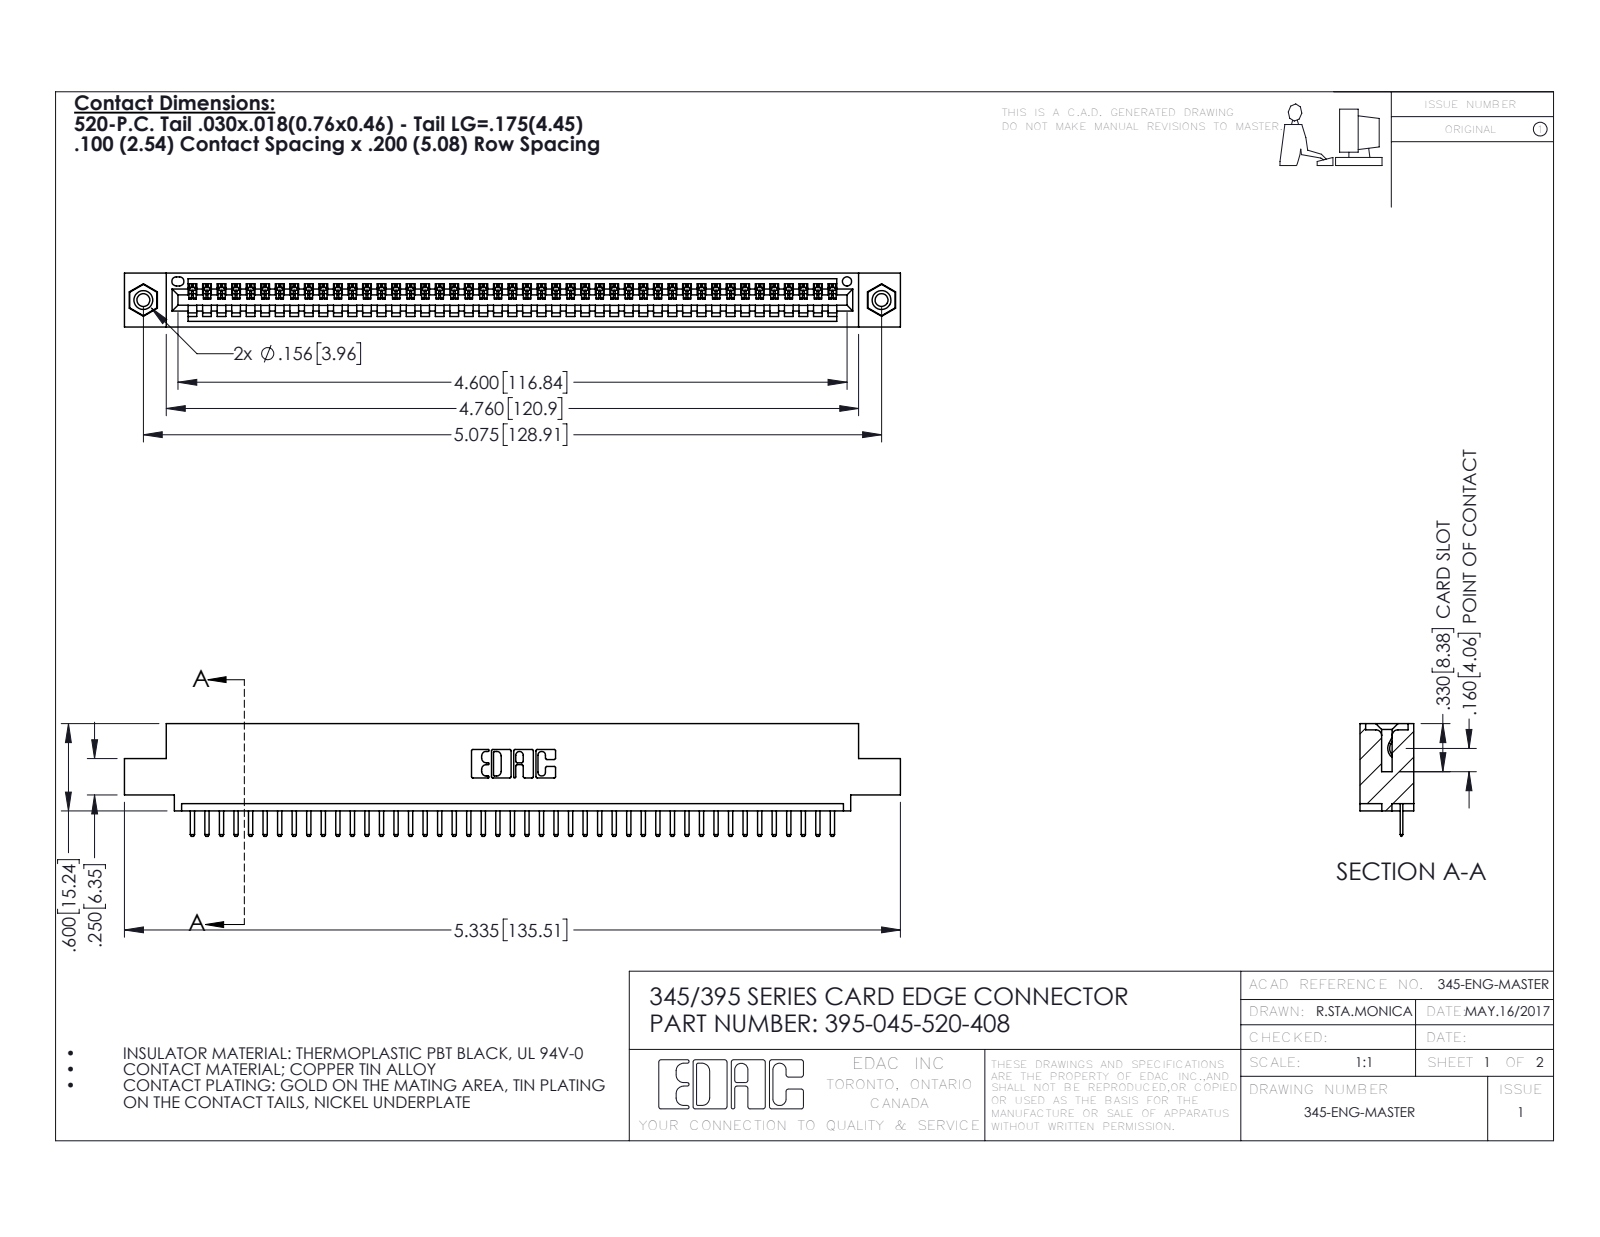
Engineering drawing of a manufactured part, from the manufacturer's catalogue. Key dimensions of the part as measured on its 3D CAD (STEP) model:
Part name (STEP PRODUCT): 345-292-001_345-293-120; 395-045-520-408; 345 Part_0.110 Offset - 0.156 Dia-TI; 345-250-001_345-250-003-102
STEP written by: SolidWorks 2016 (CONFIG_CONTROL_DESIGN)
Units: inches
Bodies: 48 solids, 2980 faces (2006 planar, 958 cylindrical, 16 other)
Overall size (bounding box): 5.335 × 0.775 × 0.37
Volume: 0.774 in³ · Surface area: 25.69 in²
Round holes (diameter × count): ⌀0.089 ×2, ⌀0.125 ×2, ⌀0.156 ×2, ⌀0.064 ×1
Round bosses / shafts (diameter × count): ⌀0.155 ×2
Partial cylindrical surfaces — rounded edges, fillets, slot ends (radius × count): R0.01 ×92, R0.006 ×90, R0.01 ×22, R0.007 ×6, R0.031 ×6, R0.026 ×3, R0.031 ×2, R0.04 ×2
Main face-to-face distances: 0.072, 0.298, 0.37, 0.2, 0.098, 0.272, 0.025, 0.225, 0.072, 0.149
Hole centre spacings: 0.27, 4.839, 5.075
